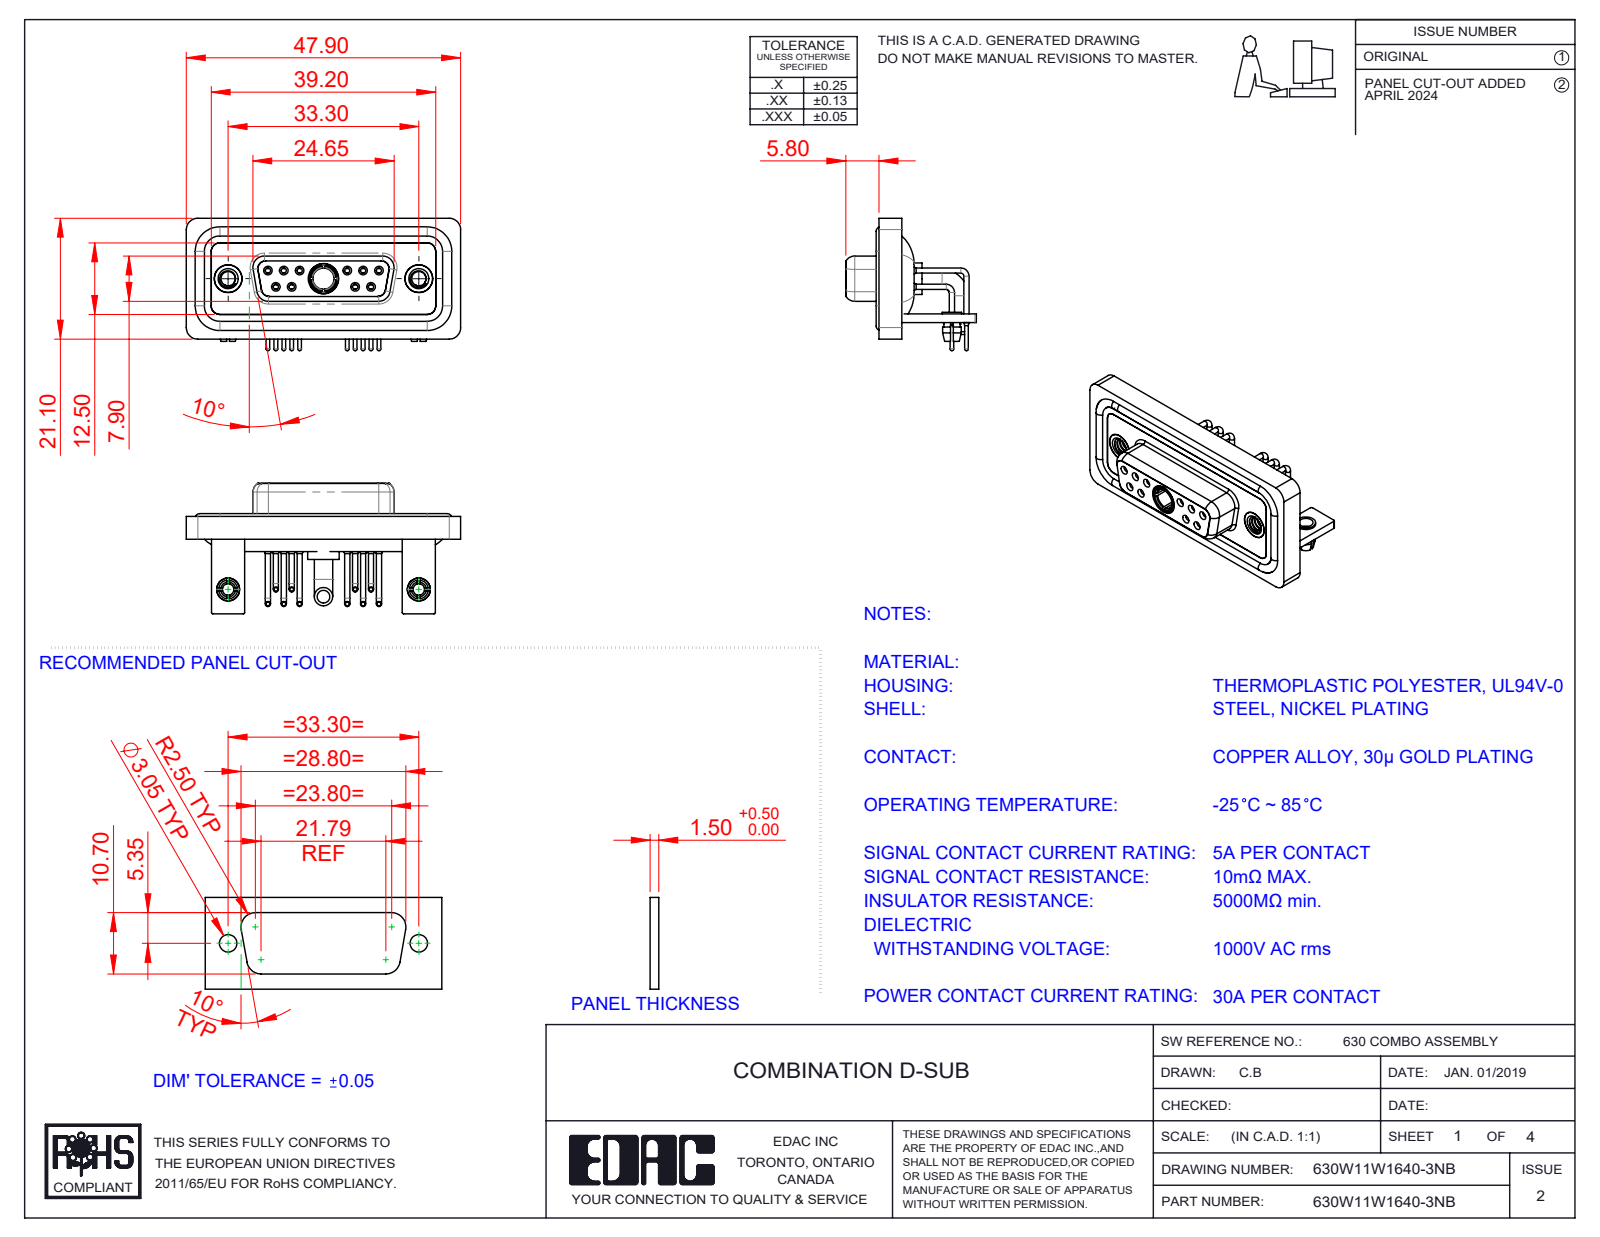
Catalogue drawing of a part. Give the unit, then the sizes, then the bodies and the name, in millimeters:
Units: millimetres
Overall size (bounding box): 47.9 × 23.12 × 22.8
Round holes (diameter × count): ⌀2 ×12, ⌀0.9 ×10, ⌀1.1 ×10, ⌀1.5 ×10, ⌀1.7 ×6, ⌀1.6 ×4, ⌀2.5 ×4, ⌀4.85 ×3, ⌀3.2 ×2, ⌀4 ×2, ⌀4.05 ×2, ⌀5 ×2
Round bosses / shafts (diameter × count): ⌀1.6 ×10, ⌀0.9 ×10, ⌀0.65 ×10, ⌀4.95 ×2, ⌀4.8 ×2, ⌀4 ×2, ⌀3.4 ×2, ⌀3.3 ×2
Partial cylindrical surfaces — rounded edges, fillets, slot ends (radius × count): R2 ×21, R1.5 ×18, R0.25 ×16, R1.35 ×12, R1.6 ×8, R0.5 ×5, R0.6 ×4, R0.65 ×4
Main face-to-face distances: 0.4, 2.9, 1.5, 1.8, 3.7, 1.1, 1.6, 4.1, 0.8, 2.5
Hole centre spacings: 3.16, 2.77, 13.85, 11.08, 16.62, 5.03, 5.04, 5.54
Volume: 6 641 mm³ · Surface area: 11 438 mm²
Bodies: 23 solids, 1128 faces (352 planar, 497 cylindrical, 279 other)
Part name (STEP PRODUCT): 630Combo Stabilizer Bracket_50 Contacts; 630Combo Waterproof Housing_15 Contacts; 630Combo Shell Front_15 Contacts; 630Combo Contact Row 2_50 Contacts (+7 more)
STEP written by: SolidWorks 2023 (CONFIG_CONTROL_DESIGN)
